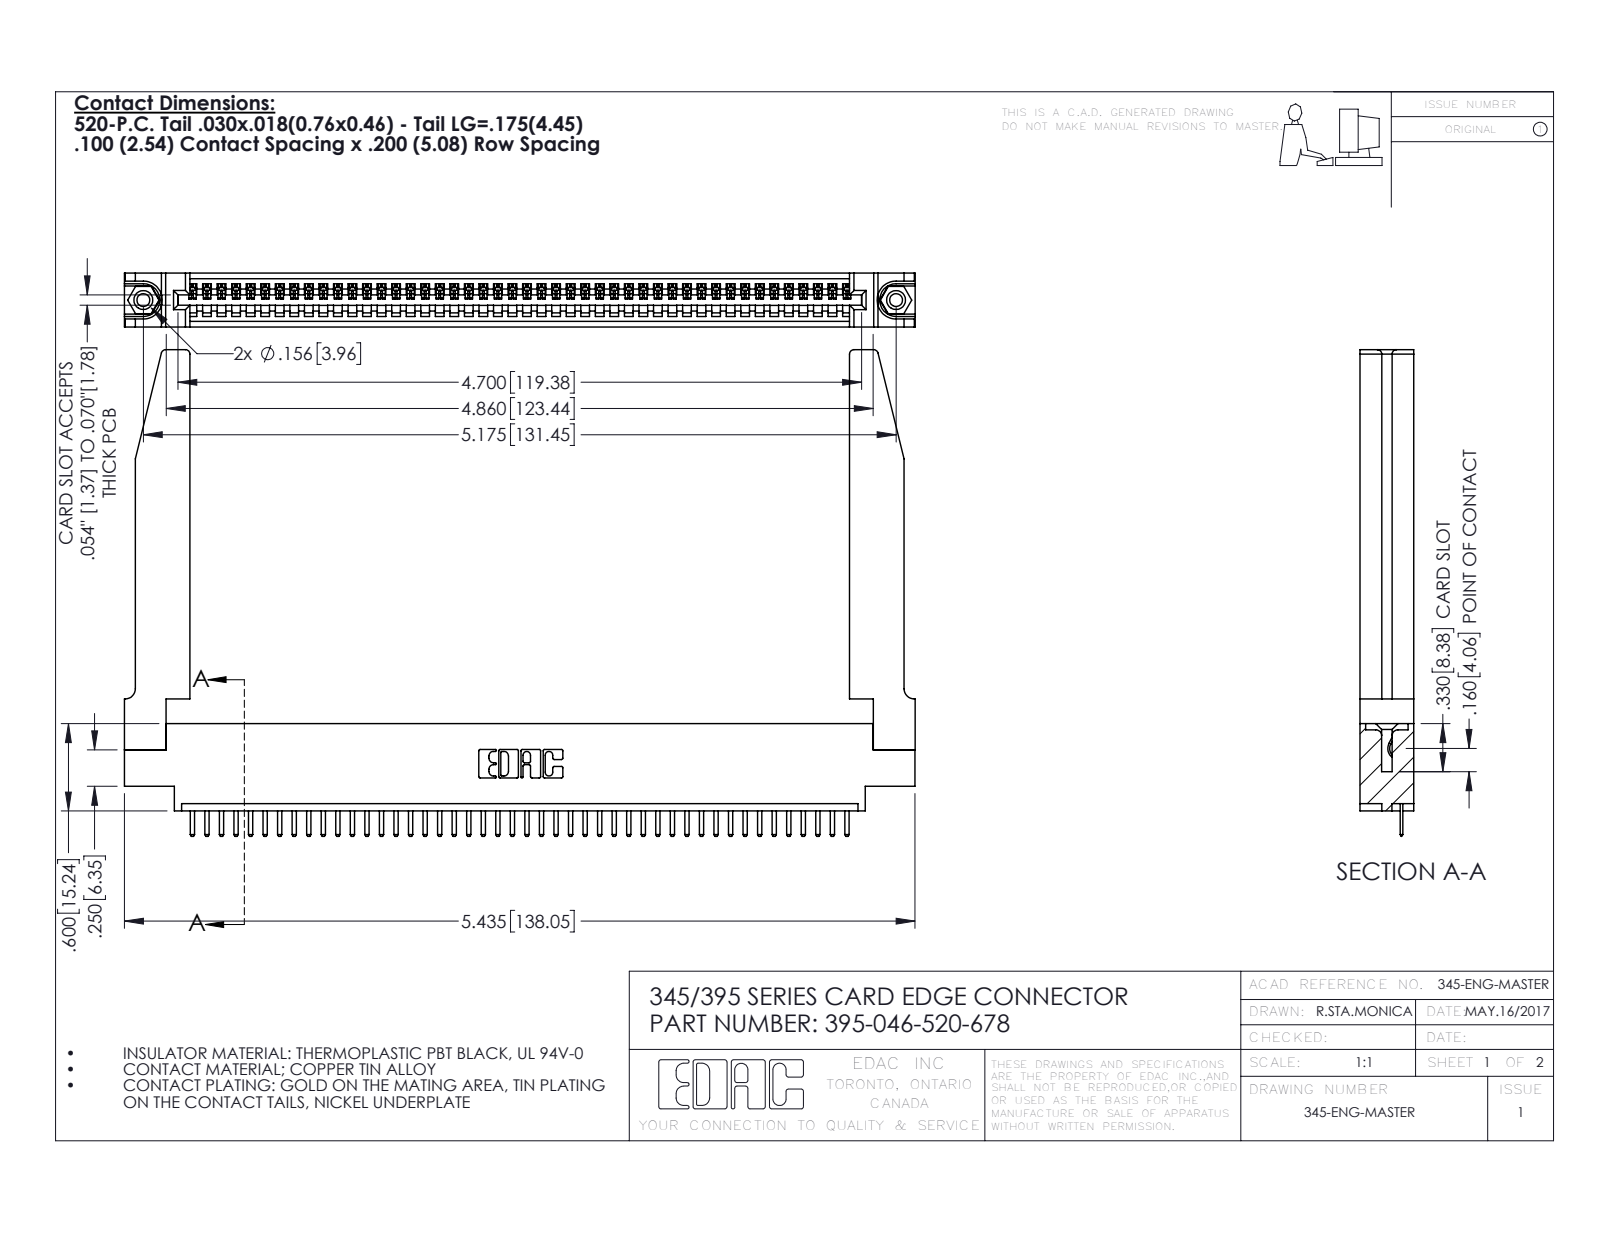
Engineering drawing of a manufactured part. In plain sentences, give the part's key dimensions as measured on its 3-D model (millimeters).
The part is named "345-220-078_345-220-078; 345-292-001_345-293-120; 395-046-520-678; 345 Part_0.170 Offset - 0.156 Dia-TH (+1 more)". Its 3-D file was written by "SolidWorks 2016 (CONFIG_CONTROL_DESIGN)". It is 51 solids with 3216 faces: 2158 planar, 1006 cylindrical and 52 other. Overall it measures 138.1 by 85 by 9.4 millimeters. Its volume is 20 660 cubic millimeters and its surface area 23 740 square millimeters. Round holes: 2 of diameter 2.3, 2 of diameter 3.2, 2 of diameter 4, 1 of diameter 1.6. Round bosses or shafts: 2 of diameter 3.9. Partial cylindrical surfaces (rounded edges, fillets, slot ends): 94 of radius 0.3, 92 of radius 0.2, 22 of radius 0.3, 8 of radius 0.8, 6 of radius 0.2, 6 of radius 0.8, 3 of radius 0.7, 2 of radius 0.8. The main face-to-face distances are 9.4, 1.8, 7.6, 5.1, 2.5, 6.9, 0.6, 5.7, 3.8, 3.8. The hole center spacings are 6.9, 125.5, 131.4.
